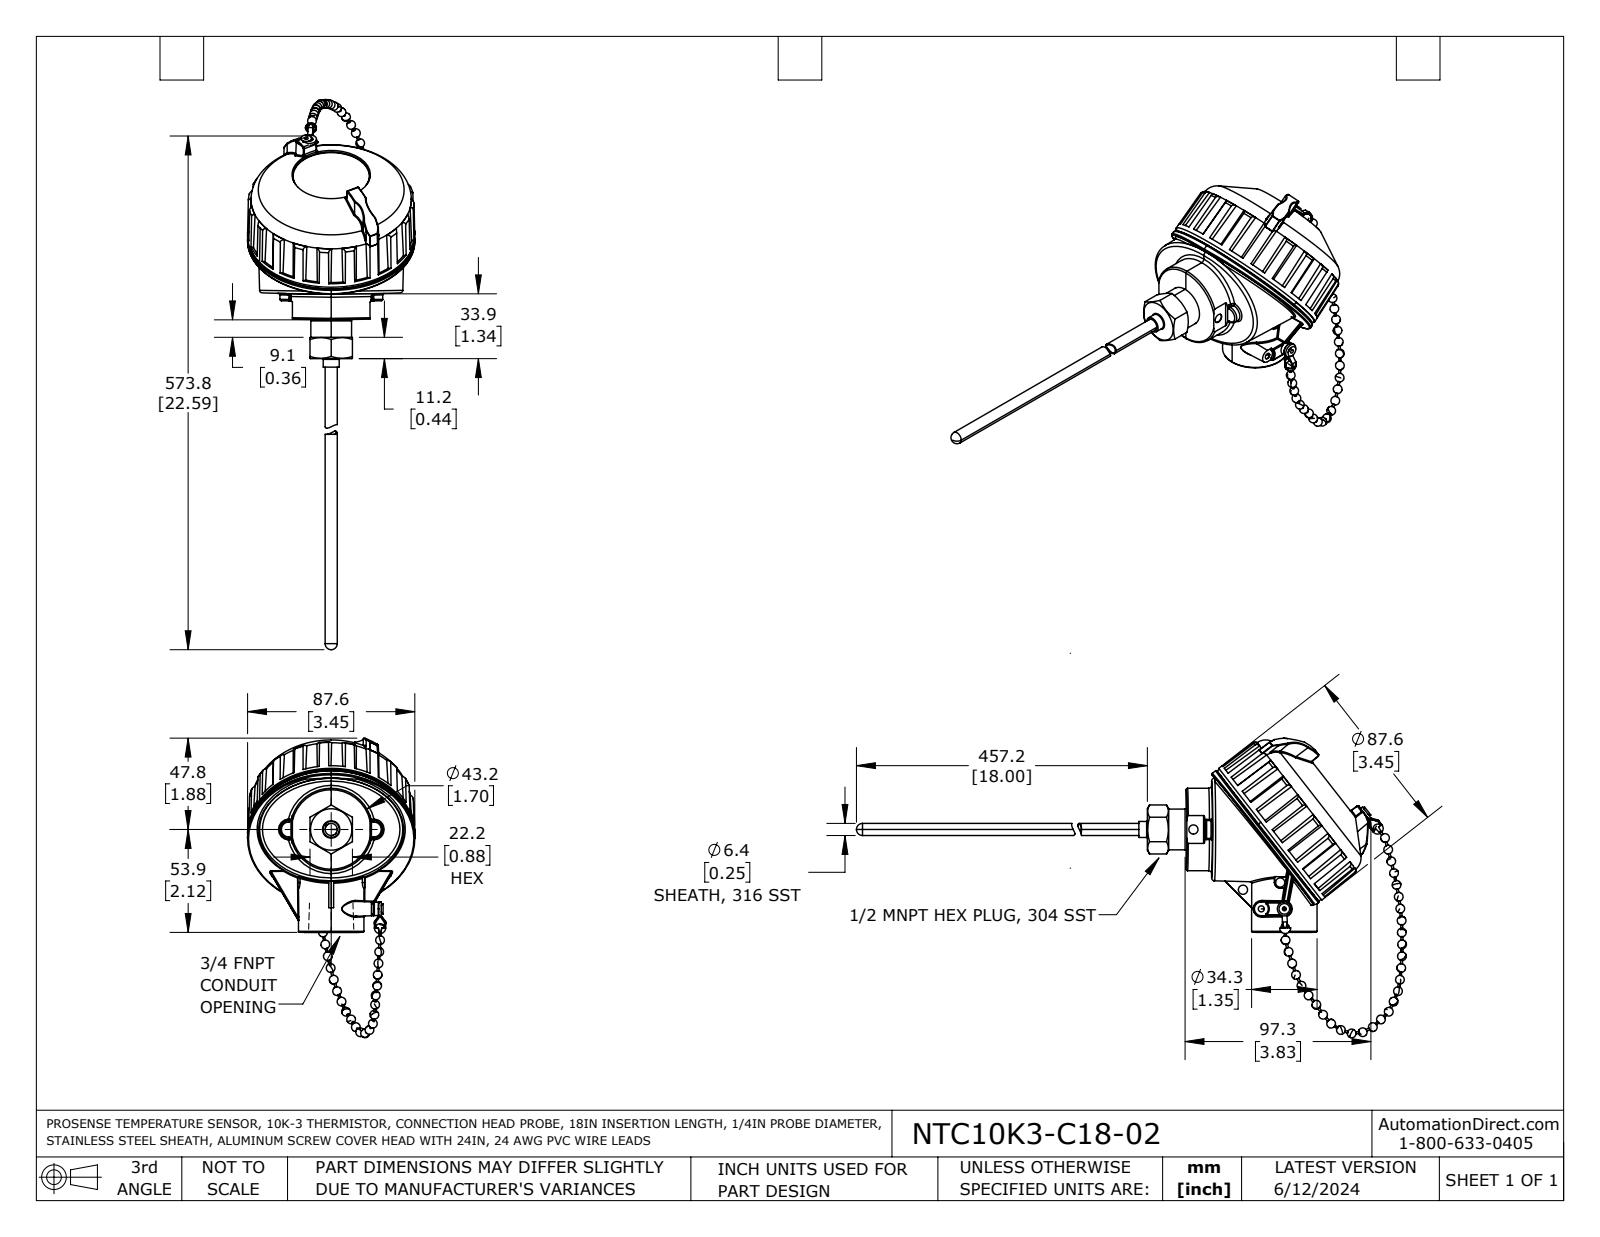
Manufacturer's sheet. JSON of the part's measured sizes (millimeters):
{"part_name": "NTC10K3-C18-02", "step_written_by": "SolidWorks 2021 (AUTOMOTIVE_DESIGN)", "units": "millimeters", "bodies": {"solids": 10, "faces": 982, "planar": 232, "cylindrical": 189, "other": 561}, "overall_size": [592.8, 156.9, 87.6], "volume_mm3": 151400, "surface_area_mm2": 89420, "round_holes": [[4.8, 3], [2, 2], [3.7, 2], [3.2, 1], [4.2, 1], [5.3, 1], [6.4, 1], [11.1, 1], [22.6, 1], [76.3, 1], [76.9, 1], [80, 1]], "round_bosses_or_shafts": [[1, 31], [7.4, 2], [3.1, 2], [87.6, 1], [86.5, 1], [79.3, 1], [76, 1], [43.2, 1]], "partial_cylinders_radius": [[0.5, 21], [0.8, 11], [0.4, 6], [1.5, 5], [4.7, 2], [1.6, 1], [3.7, 1]], "face_to_face_distances": [37.7, 36.1, 1.6, 3.6, 39.6, 41.2, 13.3, 39.6, 36.1, 1.6], "hole_center_spacings": [1.8, 12.1, 13.9, 13.9, 17, 19.9, 23.9, 25]}
